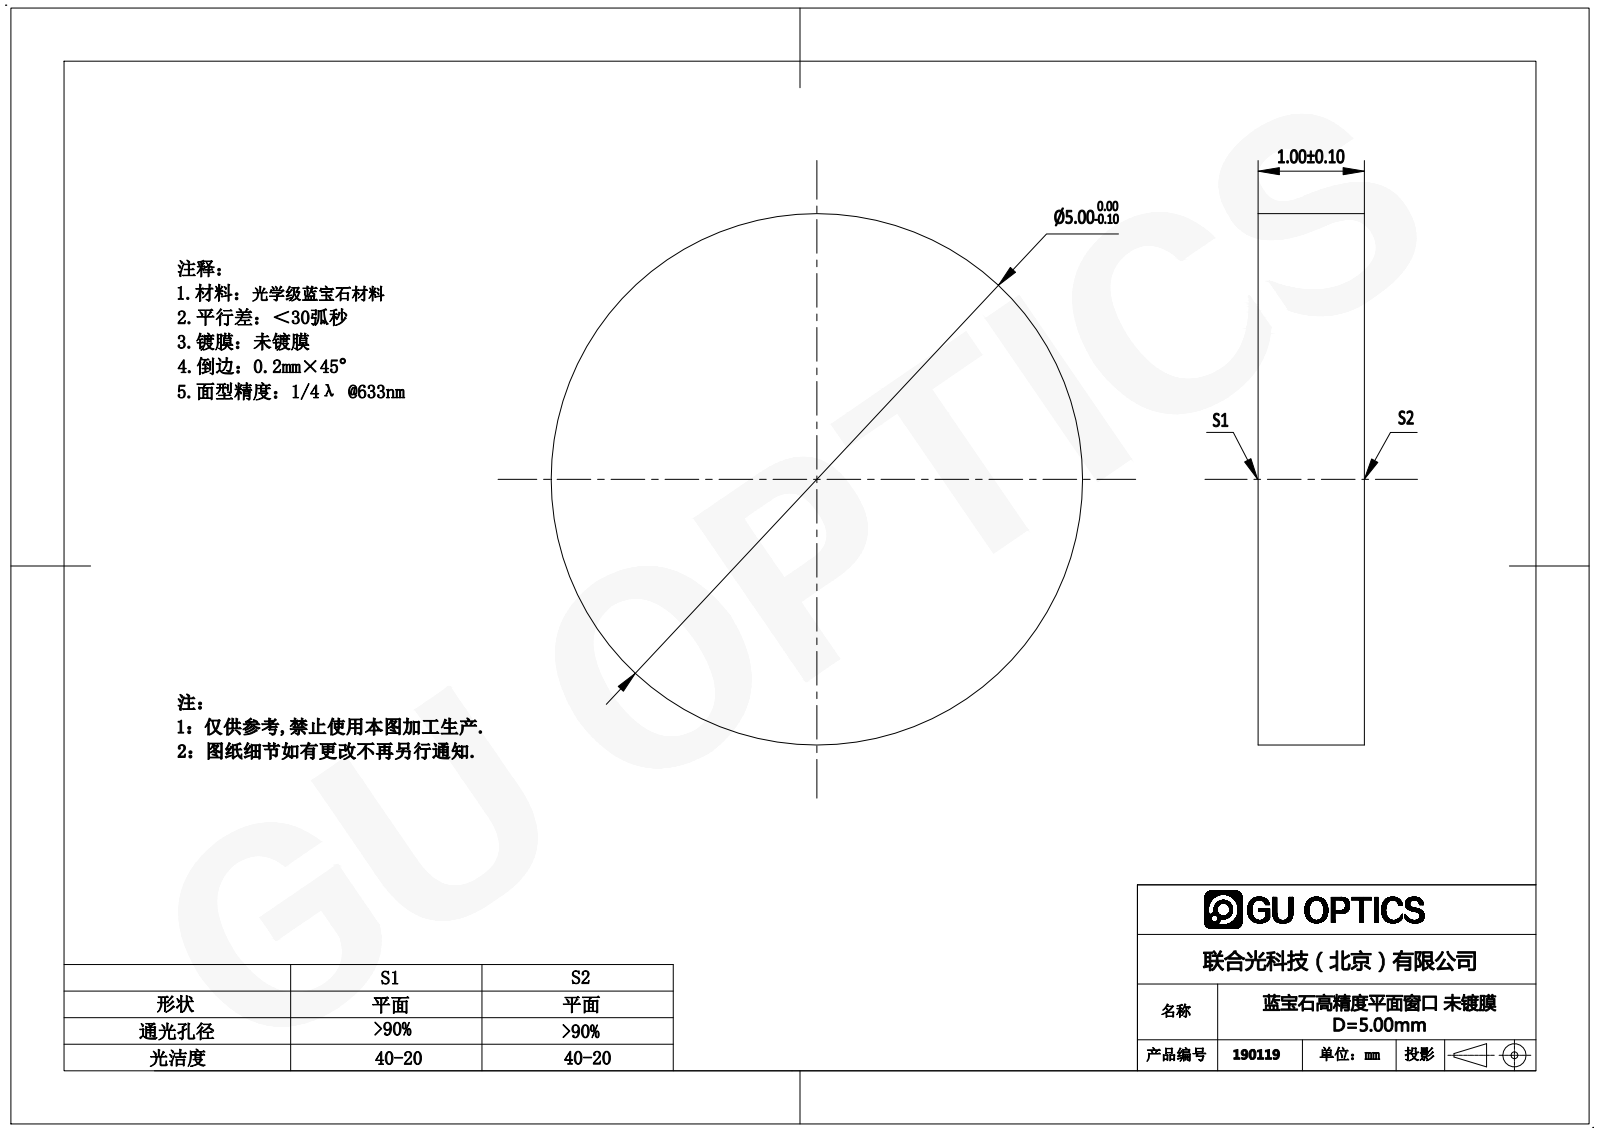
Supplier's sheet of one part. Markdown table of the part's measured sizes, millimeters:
| quantity | value |
| --- | --- |
| part name | 190119 |
| STEP written by | SolidWorks 2016 (AUTOMOTIVE_DESIGN) |
| units | millimeters |
| bodies | 1 solid, 4 faces (2 planar, 2 cylindrical, 0 other) |
| overall size | 5 × 5 × 1 |
| volume | 20 mm³ |
| surface area | 55 mm² |
| round bosses / shafts (diameter × count) | 5 × 1 |
| main face-to-face distances | 1 |
